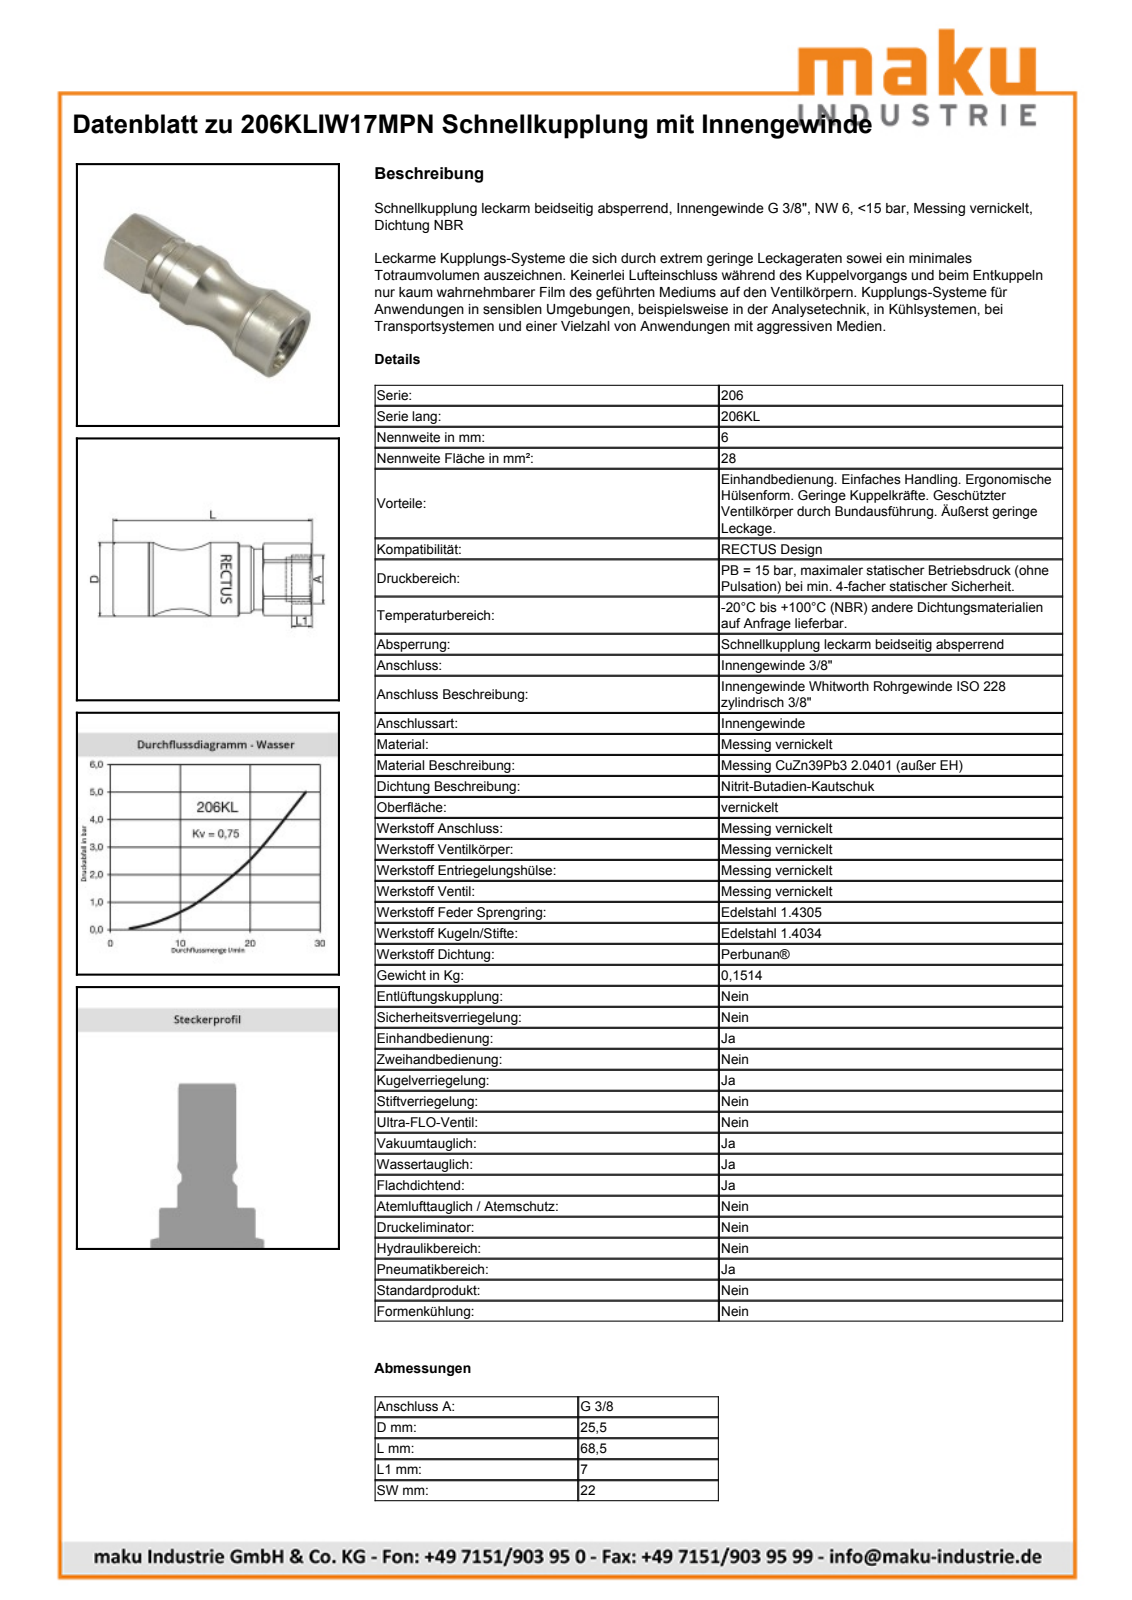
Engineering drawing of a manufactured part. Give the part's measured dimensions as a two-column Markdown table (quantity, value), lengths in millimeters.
| quantity | value |
| --- | --- |
| part name | D108001 |
| STEP written by | Autodesk Inventor 2013 (AUTOMOTIVE_DESIGN) |
| units | millimeters |
| bodies | 1 solid, 1168 faces (417 planar, 145 cylindrical, 606 other) |
| overall size | 68.5 × 25.5 × 25.5 |
| volume | 23 982 mm³ |
| surface area | 13 985 mm² |
| round holes (diameter × count) | 10.2 × 1, 14.95 × 1, 18.1 × 1, 18.15 × 1, 18.25 × 1, 19.7 × 1, 20.05 × 1, 20.9 × 1, 21.3 × 1, 23.1 × 1, 23.55 × 1, 24.1 × 1 |
| round bosses / shafts (diameter × count) | 25.5 × 1, 25.3 × 1, 23.4 × 1, 23 × 1, 21 × 1, 20 × 1, 18 × 1, 16.65 × 1 |
| partial cylindrical surfaces (radius × count) | 12.4 × 1 |
| main face-to-face distances | 22, 22.02, 68.5, 4.1, 8, 4.65, 59.5, 9, 1.3, 58.2 |
